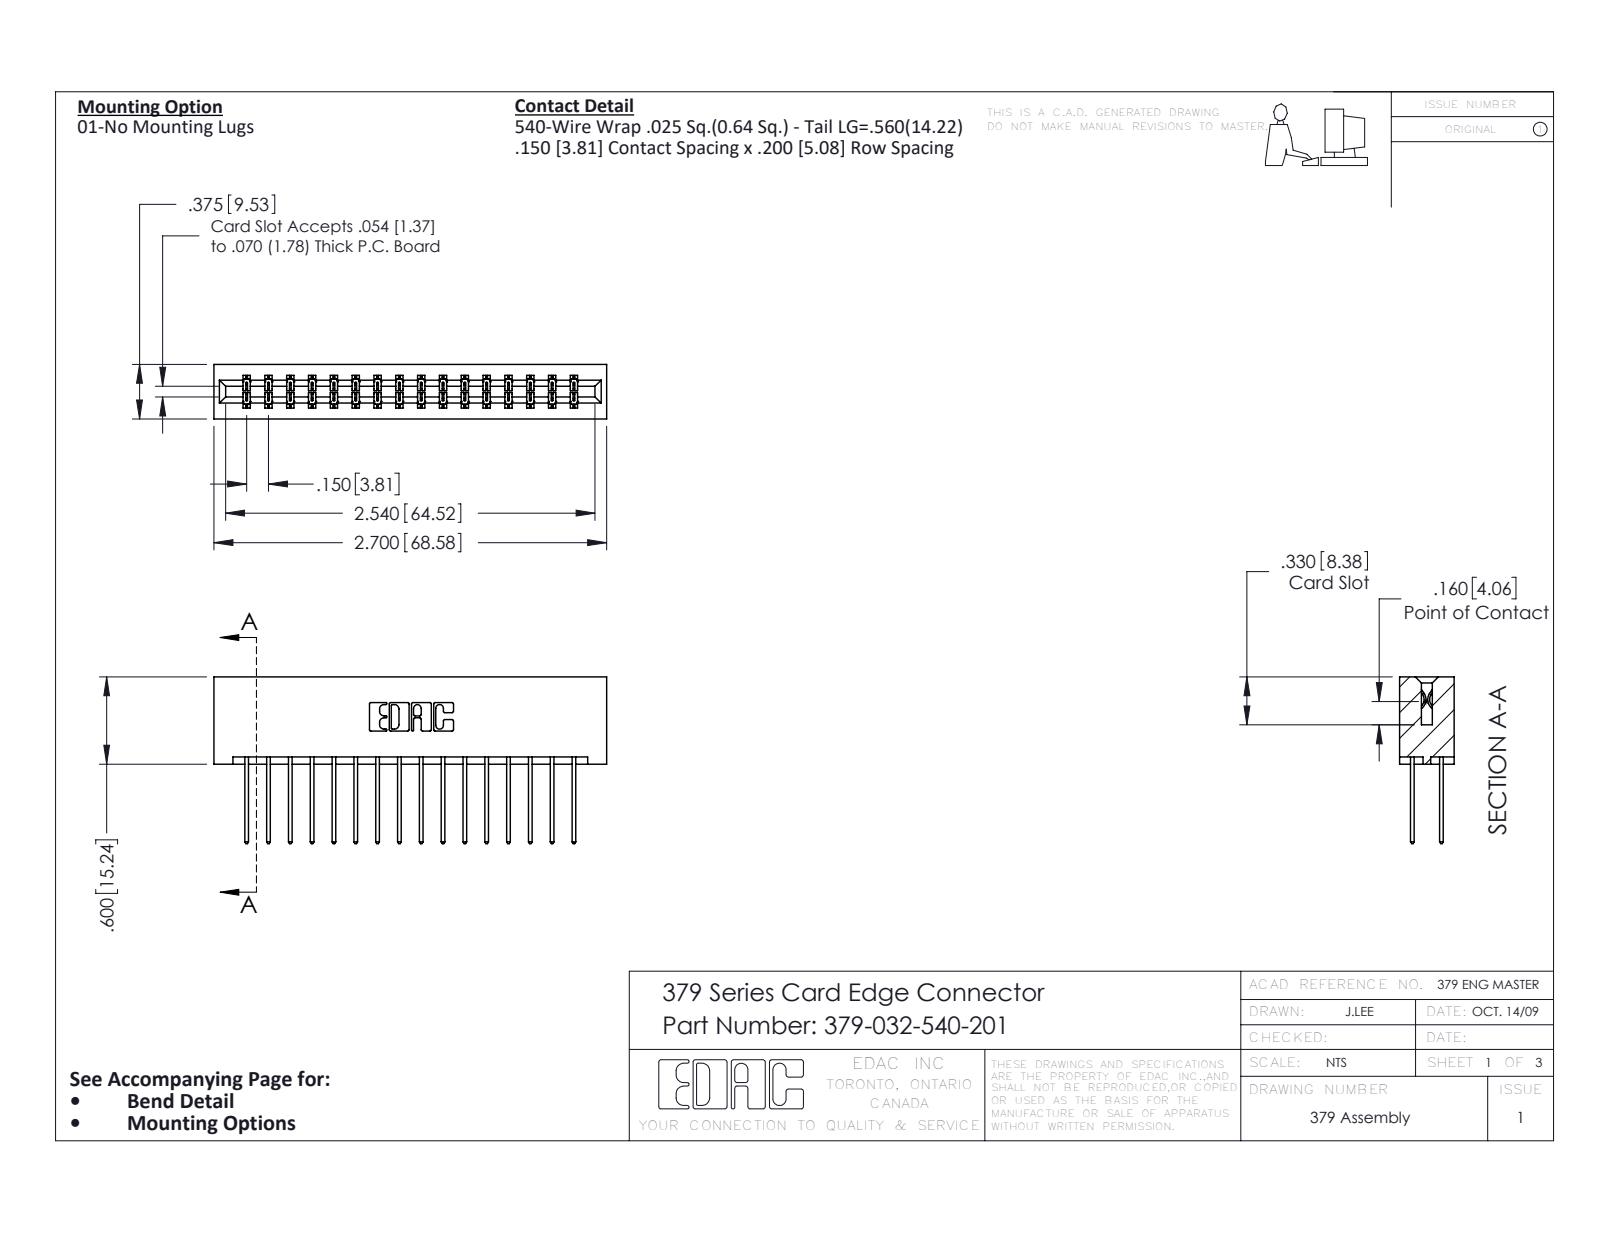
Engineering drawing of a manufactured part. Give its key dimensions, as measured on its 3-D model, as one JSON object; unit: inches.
{"part_name": "379 Part_Lugless; 345-292-001_345-293-140; 379-032-540-201", "step_written_by": "SolidWorks 2020 (CONFIG_CONTROL_DESIGN)", "units": "inches", "bodies": {"solids": 33, "faces": 1770, "planar": 1218, "cylindrical": 552, "other": 0}, "overall_size": [2.7, 1.147, 0.375], "volume_in3": 0.479, "surface_area_in2": 14.27, "partial_cylinders_radius": [[0.006, 48], [0.01, 32], [0.01, 22], [0.007, 6], [0.031, 6], [0.026, 3], [0.014, 2], [0.022, 2]], "face_to_face_distances": [0.3, 0.075, 0.1, 0.2, 0.375, 0.15, 0.275, 0.55, 0.6, 0.025]}
